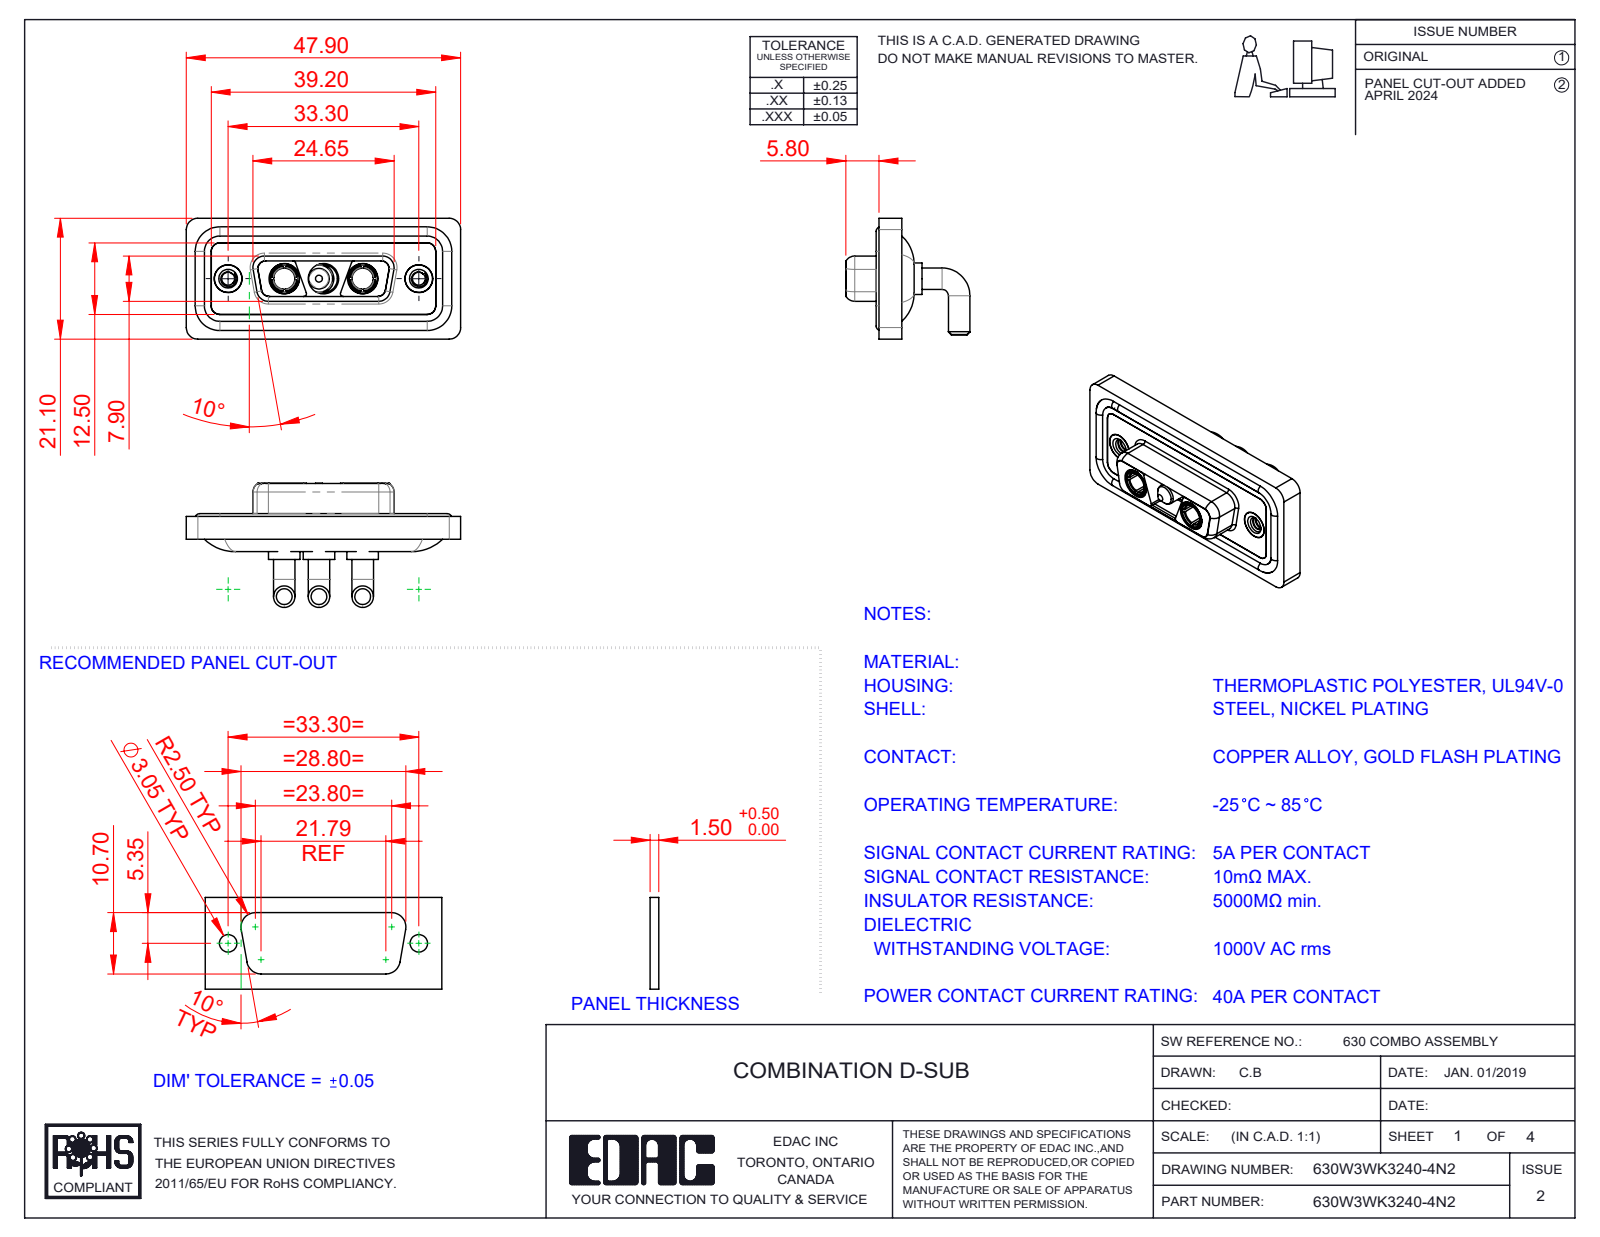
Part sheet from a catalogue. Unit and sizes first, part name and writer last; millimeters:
Units: millimetres
Overall size (bounding box): 47.9 × 21.68 × 21.1
Round holes (diameter × count): ⌀4.85 ×5, ⌀5.3 ×3, ⌀2.26 ×2, ⌀3.7 ×2, ⌀4 ×2, ⌀4.05 ×2, ⌀5 ×2
Round bosses / shafts (diameter × count): ⌀3.75 ×6, ⌀1.6 ×4, ⌀5.5 ×3, ⌀5.2 ×3, ⌀4.75 ×3, ⌀4.96 ×2, ⌀4.95 ×2, ⌀4.8 ×2
Partial cylindrical surfaces — rounded edges, fillets, slot ends (radius × count): R2 ×20, R1.5 ×18, R1.35 ×12, R0.5 ×8, R1.6 ×8, R0.25 ×4, R0.6 ×4, R0.65 ×4
Main face-to-face distances: 0.4, 1.8, 1.1, 1.6, 2.9, 2.5, 3.1, 3.7, 4.1, 1.5
Hole centre spacings: 6.85, 9.8, 16.65, 23.5, 13.7, 33.3
Volume: 6 250 mm³ · Surface area: 9 870 mm²
Bodies: 13 solids, 595 faces (178 planar, 264 cylindrical, 153 other)
Part name (STEP PRODUCT): 630W3WK3240-4N2; 630Combo Housing_3WK3; 630Combo Shell Rear_15 Contacts; Power Pin_40A RA (+4 more)
STEP written by: SolidWorks 2023 (CONFIG_CONTROL_DESIGN)
